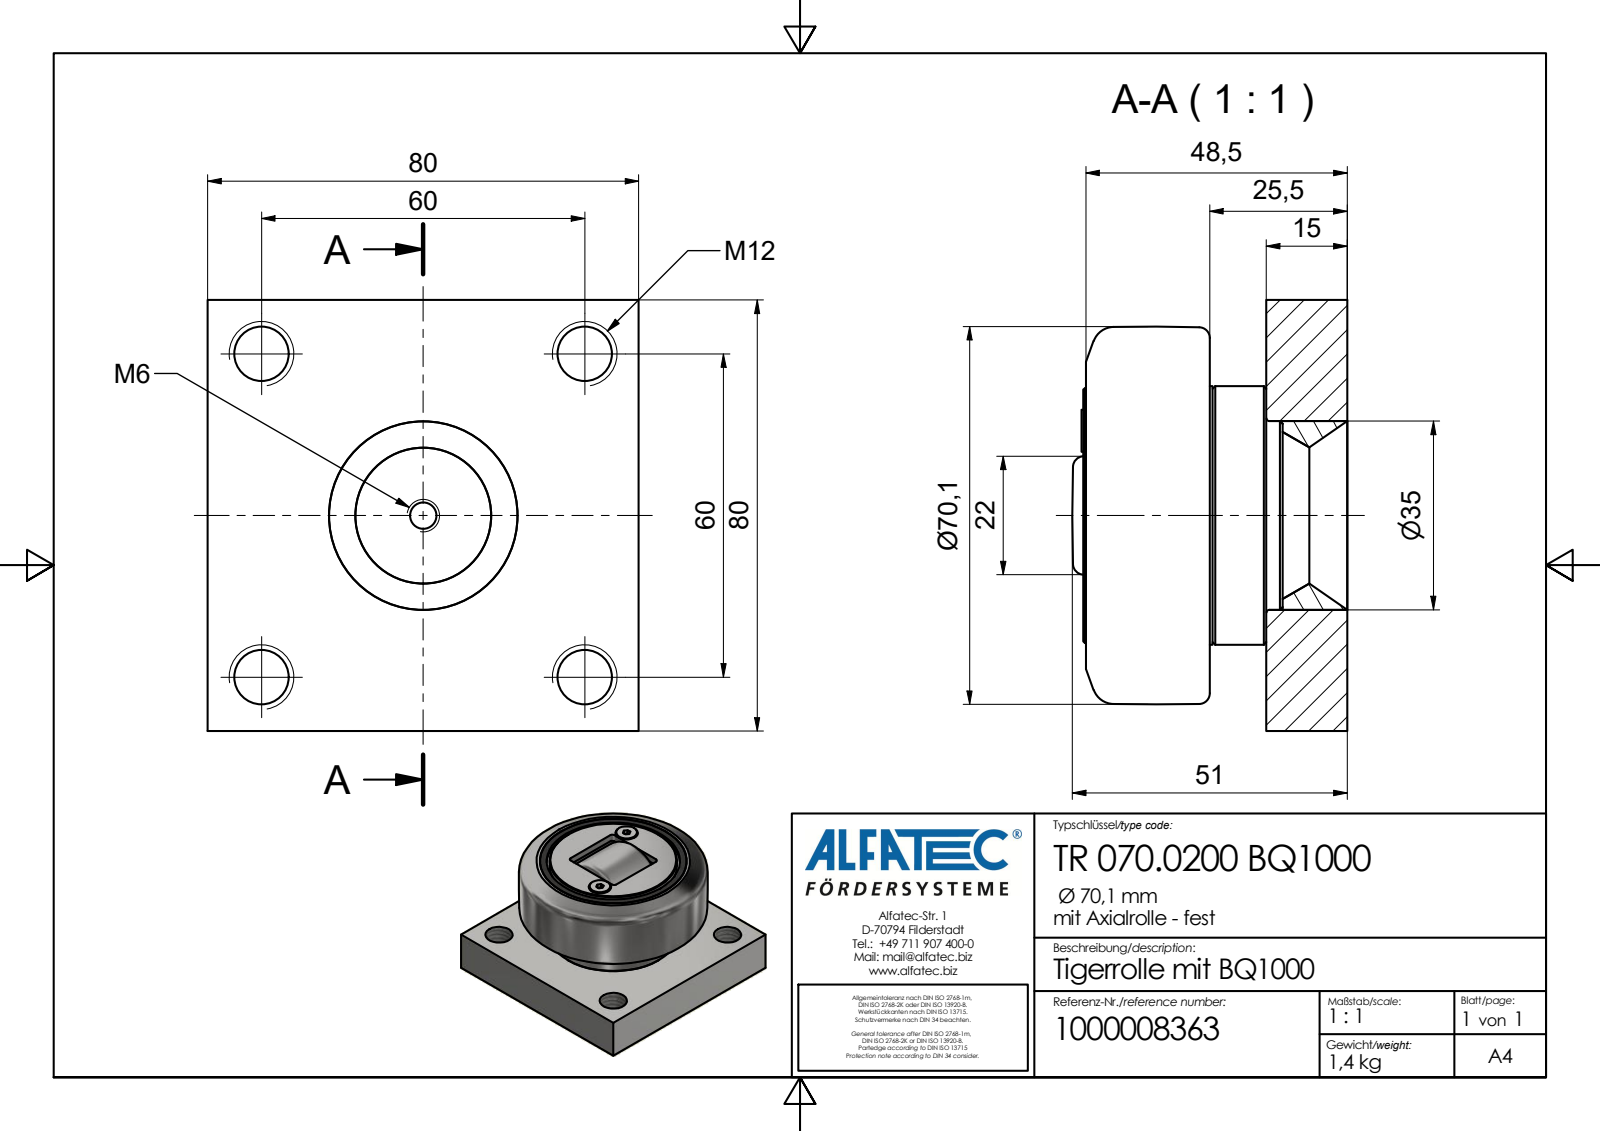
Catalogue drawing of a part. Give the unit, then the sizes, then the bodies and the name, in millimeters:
Units: millimetres
Overall size (bounding box): 80 × 80 × 51
Round holes (diameter × count): ⌀10.11 ×4, ⌀2.5 ×1, ⌀4.92 ×1
Round bosses / shafts (diameter × count): ⌀7.8 ×2, ⌀48 ×1, ⌀47.3 ×1
Partial cylindrical surfaces — rounded edges, fillets, slot ends (radius × count): R1 ×4
Main face-to-face distances: 15, 80, 25.5, 10.5, 23.5, 0.5, 49, 34, 23, 48.5
Hole centre spacings: 42.43, 60, 84.85
Volume: 192 558 mm³ · Surface area: 29 829 mm²
Bodies: 1 solid, 64 faces (36 planar, 15 cylindrical, 13 other)
Part name (STEP PRODUCT): TR 070.0200 BQ1000_Kontur
STEP written by: Autodesk Inventor 2020 (AP242_MANAGED_MODEL_BASED_3D_ENGINEERING_MIM_LF)
